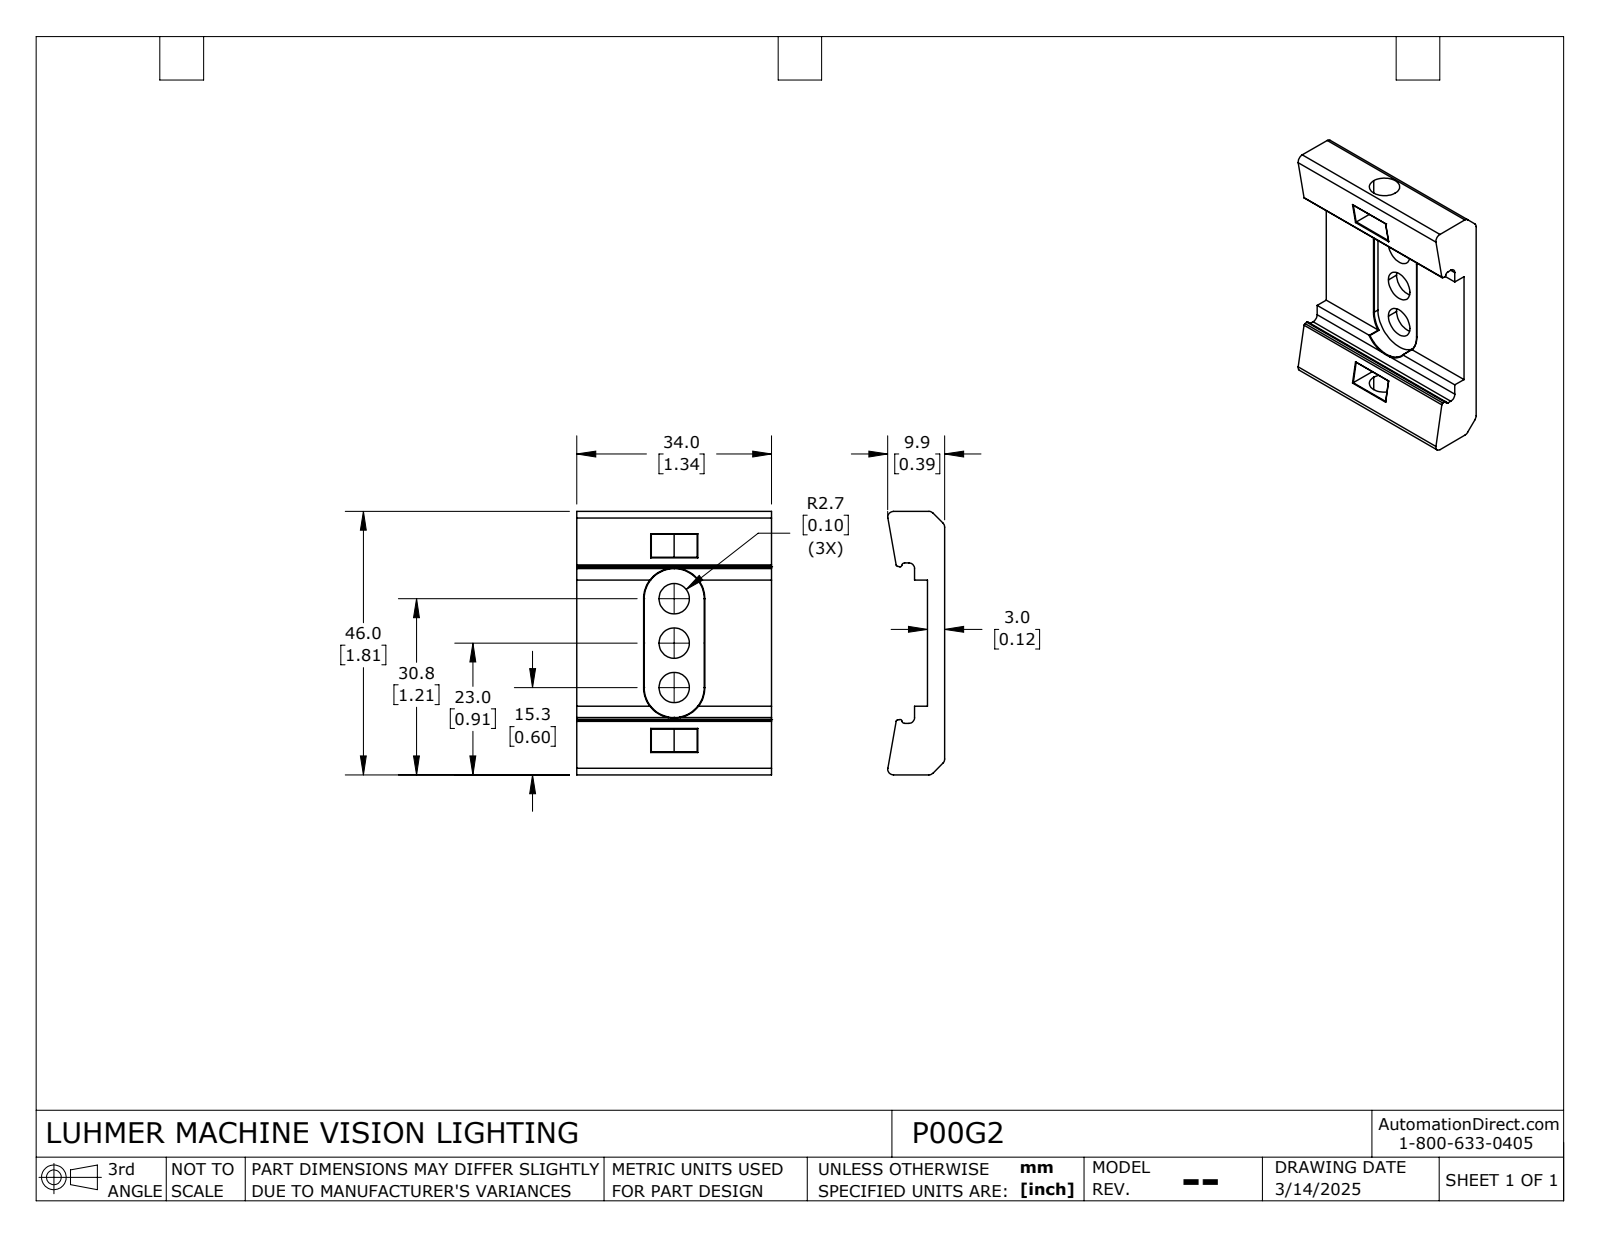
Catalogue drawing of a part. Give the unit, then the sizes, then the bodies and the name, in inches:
Units: inches
Overall size (bounding box): 1.811 × 1.339 × 0.391
Round holes (diameter × count): ⌀0.209 ×4
Partial cylindrical surfaces — rounded edges, fillets, slot ends (radius × count): R0.004 ×14, R0.039 ×8, R0.012 ×4, R0.02 ×2, R0.207 ×2
Main face-to-face distances: 0.118, 1.339, 0.157, 0.039, 0.315, 1.811, 0.079, 1.496, 1.181, 0.472
Hole centre spacings: 0.305, 0.61
Volume: 0.477 in³ · Surface area: 7.755 in²
Bodies: 1 solid, 90 faces (38 planar, 42 cylindrical, 10 other)
Part name (STEP PRODUCT): P00G2
STEP written by: SolidWorks 2024 (AUTOMOTIVE_DESIGN)
